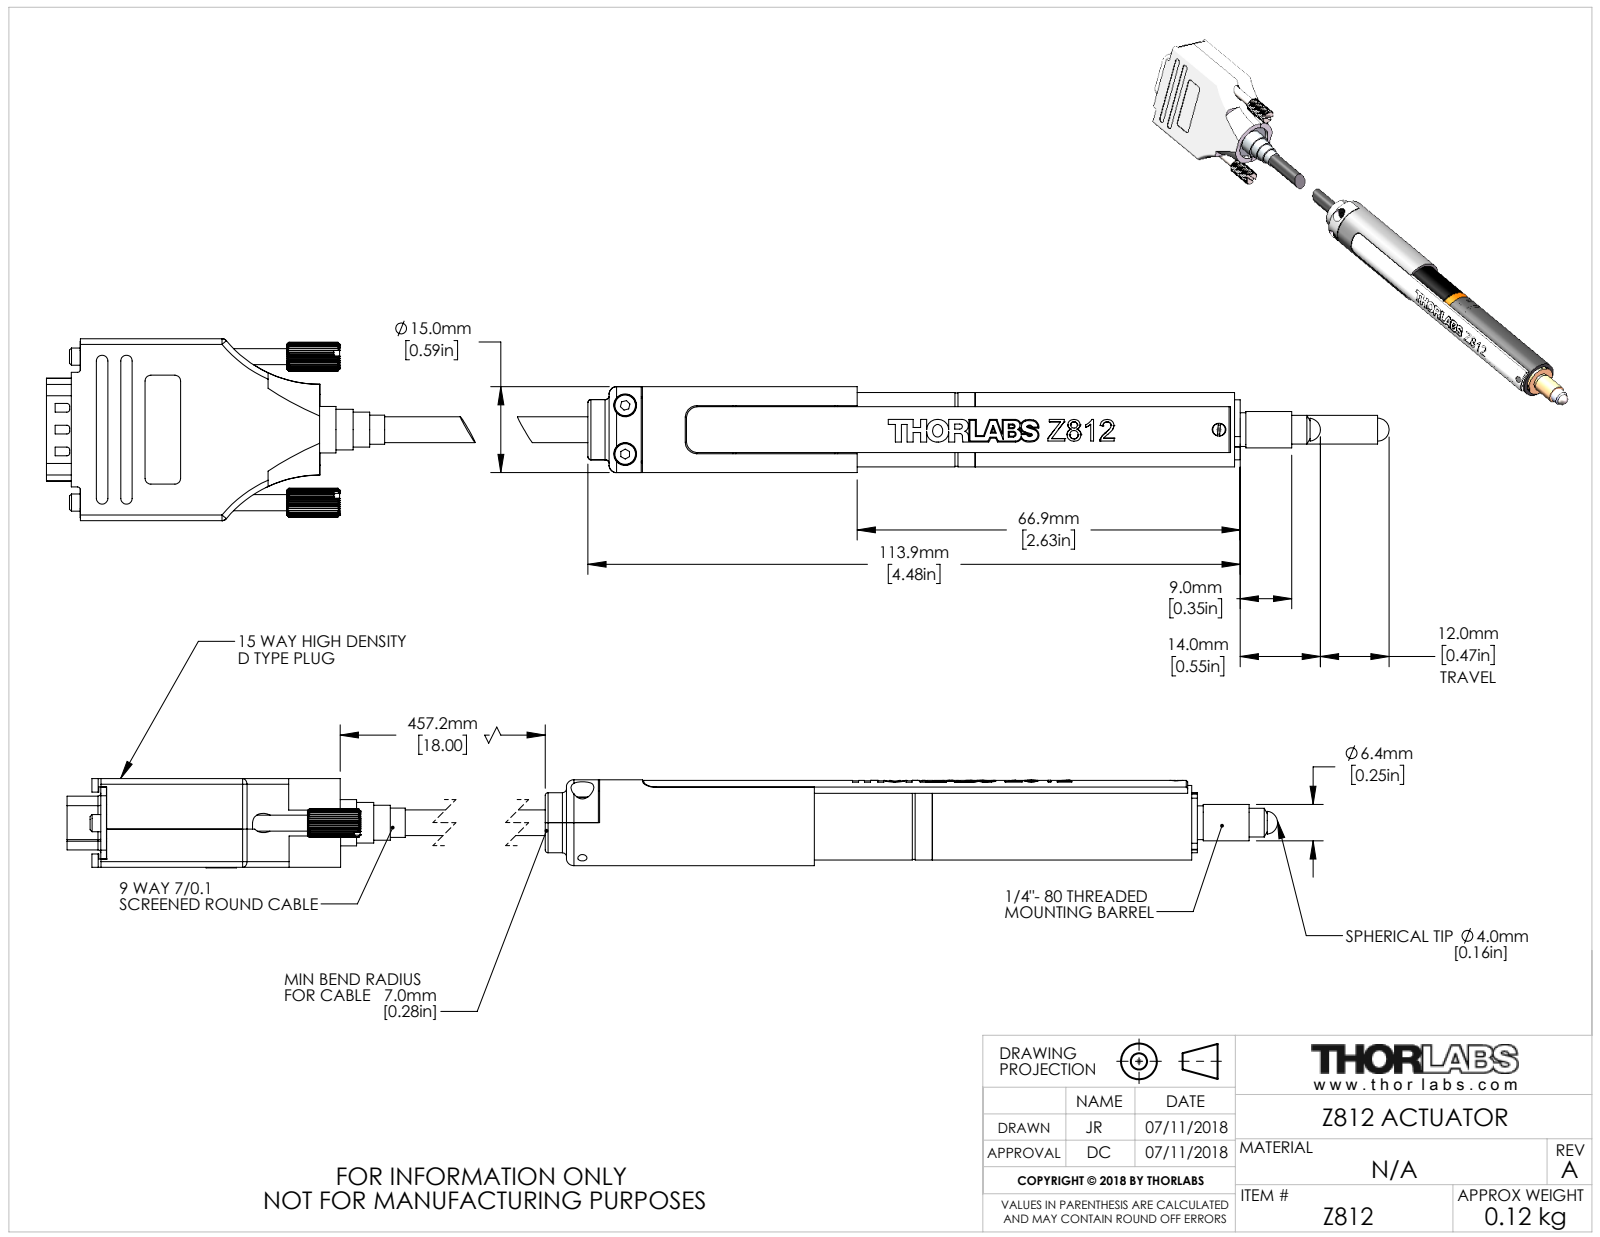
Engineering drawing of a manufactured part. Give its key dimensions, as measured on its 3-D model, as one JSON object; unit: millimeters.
{"part_name": "136001 - Z8 connector backshell; BB0692 - 9 Way D Type Shell; BD0060 - HDT001 Micro Mini SMD switch; 134348 - Z8 motor (+8 more)", "step_written_by": "SolidWorks 2014 (CONFIG_CONTROL_DESIGN)", "units": "millimeters", "bodies": {"solids": 34, "faces": 1778, "planar": 896, "cylindrical": 652, "other": 230}, "overall_size": [225.38, 31, 15], "volume_mm3": 25038, "surface_area_mm2": 29467, "round_holes": [[1.02, 15], [1.6, 4], [2.1, 4], [3.05, 4], [0.95, 2], [1.2, 2], [2.26, 2], [2.7, 2], [3.43, 2], [4, 2], [1.3, 1], [1.5, 1]], "round_bosses_or_shafts": [[1.52, 15], [0.99, 15], [2, 4], [2.2, 3], [5.56, 2], [4.97, 2], [3.8, 2], [3.77, 2]], "partial_cylinders_radius": [[0.25, 24], [0.5, 17], [0.51, 14], [0.38, 12], [1.52, 12], [0.17, 8], [1, 8], [2, 8]], "face_to_face_distances": [1.39, 13.59, 7.49, 6.1, 12.2, 14.98, 1.04, 0.35, 14.63, 7.14], "hole_center_spacings": [2.28, 3.96, 4.57, 2.29, 6.05, 6.04, 8.24, 6.86]}
